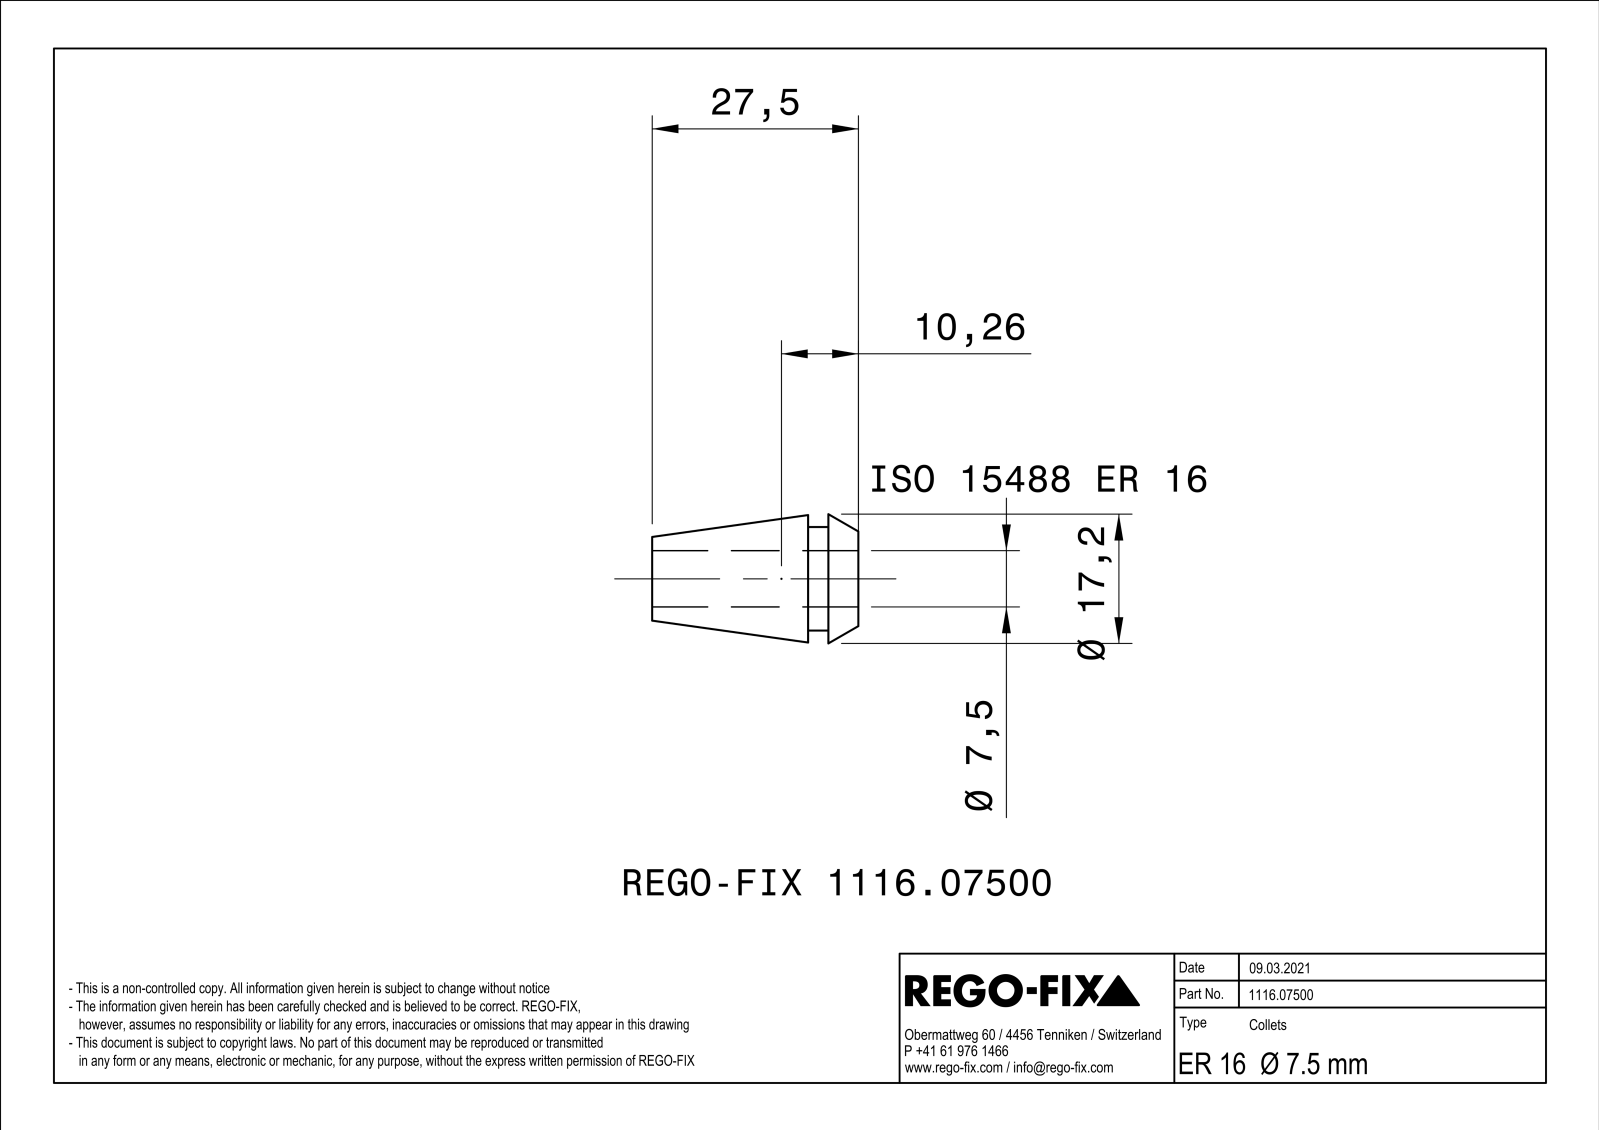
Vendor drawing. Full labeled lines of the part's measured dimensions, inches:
Part name (STEP PRODUCT): NOCUT
STEP written by: SIEMENS PLM Software Solid Edge ST10 (AUTOMOTIVE_DESIGN)
Units: inches
Bodies: 1 solid, 153 faces (72 planar, 25 cylindrical, 56 other)
Overall size (bounding box): 1.083 × 0.679 × 0.679
Volume: 0.146 in³ · Surface area: 6.674 in²
Round holes (diameter × count): ⌀0.295 ×1
Round bosses / shafts (diameter × count): ⌀0.543 ×1
Partial cylindrical surfaces — rounded edges, fillets, slot ends (radius × count): R0.012 ×8
Main face-to-face distances: 0.024, 0.157, 0.264, 0.106, 1.083, 0.925, 0.819
